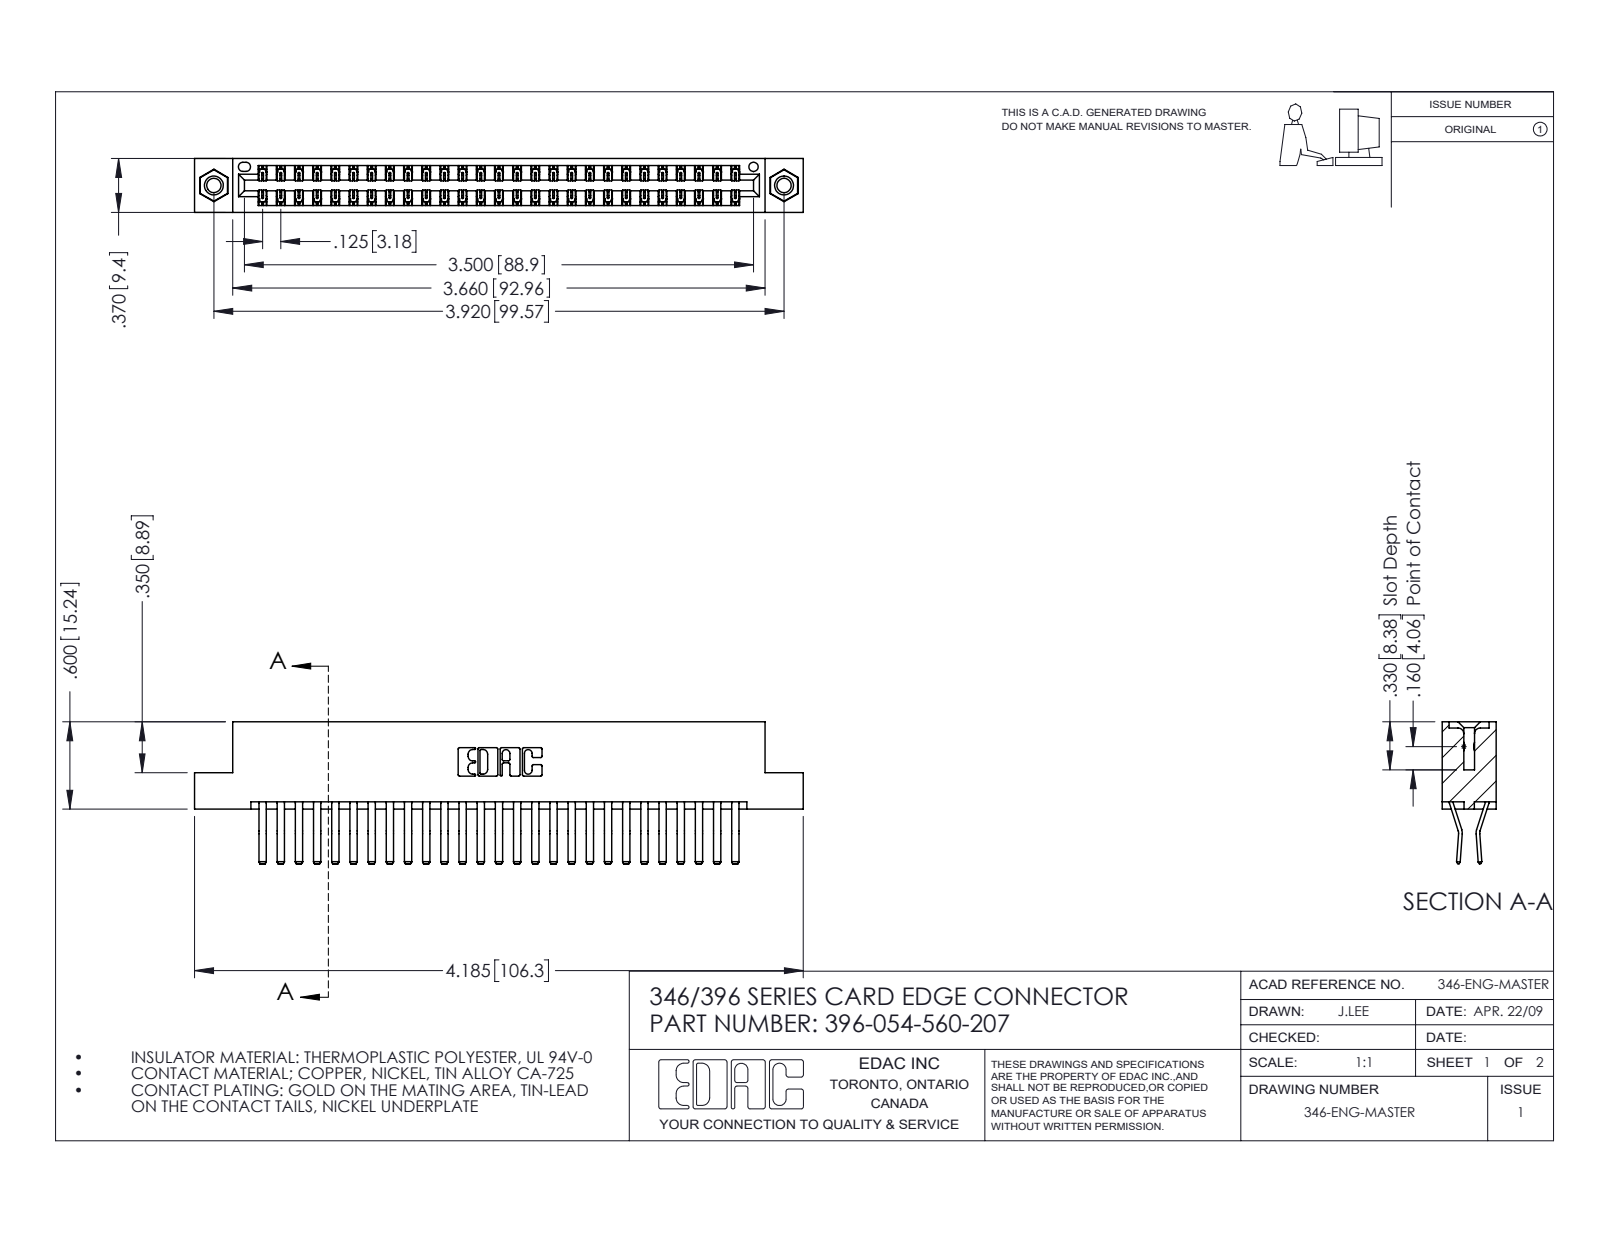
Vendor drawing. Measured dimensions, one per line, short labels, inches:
name: 346 Part_Flush Mounting Lugs - 0.156 Dia-TI; 396-054-560-208; 345-292-001_560 Tail; 345-250-001_345-250-005-103
written by: SolidWorks 2016 (CONFIG_CONTROL_DESIGN)
unit: in
bodies: 57 solids, 3098 faces (1998 planar, 1084 cylindrical, 16 other)
size: 4.185 × 0.975 × 0.37
volume: 0.646 in³; area: 23.71 in²
holes: 2× ⌀0.098, 2× ⌀0.125, 2× ⌀0.156, 1× ⌀0.064
bosses: 2× ⌀0.155
rounds: 81× R0.006, 22× R0.01, 6× R0.007, 6× R0.031, 3× R0.026, 2× R0.01, 2× R0.014, 2× R0.022
face distances: 0.048, 0.322, 0.37, 0.25, 0.025, 0.072, 0.298, 0.275, 0.148, 0.222
hole spacings: 0.246, 3.712, 3.92
